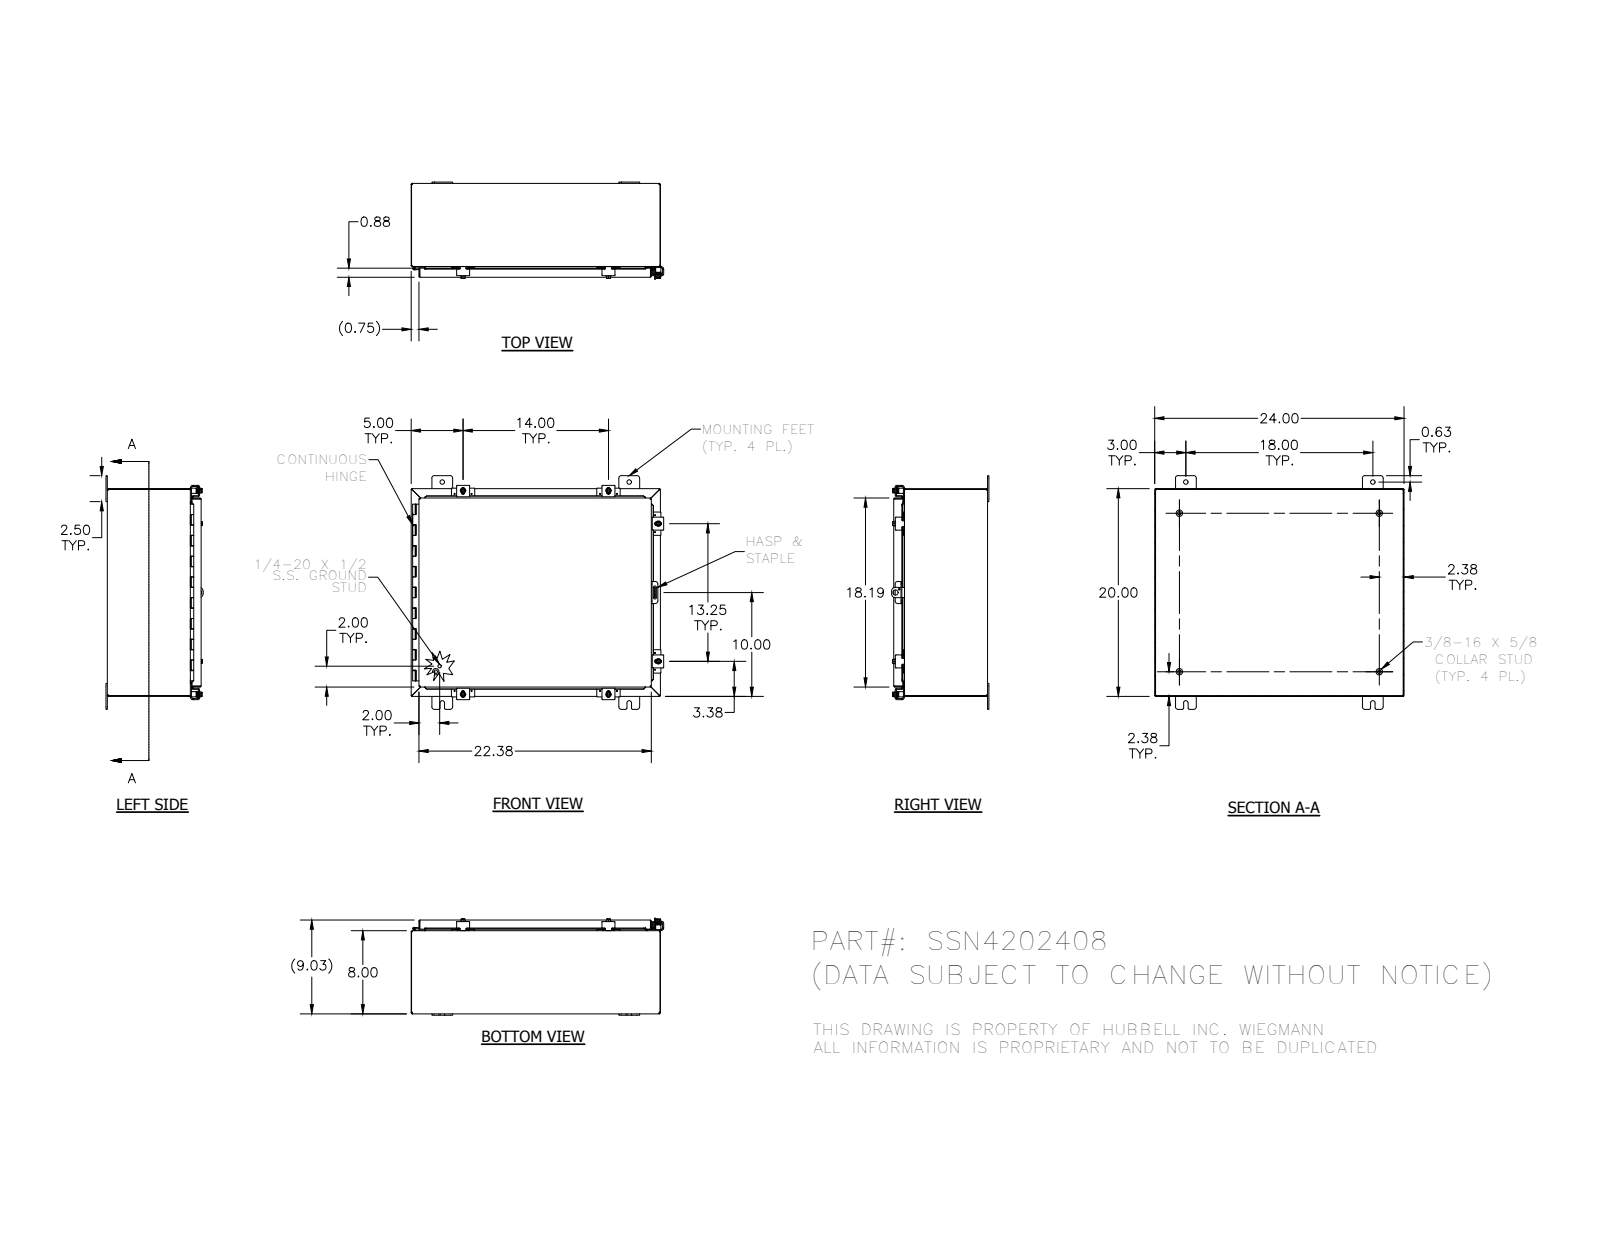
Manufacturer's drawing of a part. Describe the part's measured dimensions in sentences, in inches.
The part is named "18x22_1; HFW30825-3_1; SSN42024LID_1; HFW30825-4_1 (+8 more)". Its 3-D file was written by "SolidWorks 2014 (AUTOMOTIVE_DESIGN)". It is 47 solids with 1812 faces: 689 planar, 794 cylindrical and 329 other. Overall it measures 24.311 by 22.5 by 9.355 inches. Its volume is 153.2 cubic inches and its surface area 4 009 square inches. Round holes: 12 of diameter 0.11, 6 of diameter 0.211, 6 of diameter 0.281, 6 of diameter 0.3, 4 of diameter 0.438, 1 of diameter 0.125, 1 of diameter 0.156, 1 of diameter 0.5. Round bosses or shafts: 8 of diameter 0.25, 6 of diameter 0.52, 6 of diameter 0.5, 6 of diameter 0.35, 4 of diameter 0.625, 4 of diameter 0.33, 2 of diameter 0.115, 1 of diameter 0.337. Partial cylindrical surfaces (rounded edges, fillets, slot ends): 71 of radius 0.03, 35 of radius 0.125, 31 of radius 0.25, 23 of radius 0.031, 23 of radius 0.105, 13 of radius 0.062, 12 of radius 0.141, 8 of radius 0.07. The main face-to-face distances are 0.074, 8.959, 8.885, 9.033, 19.926, 23.926, 7.926, 1.033, 20, 19.852. The hole center spacings are 0.876, 19.306, 14, 1.625, 13.191, 14.816, 18.961, 19.03.
